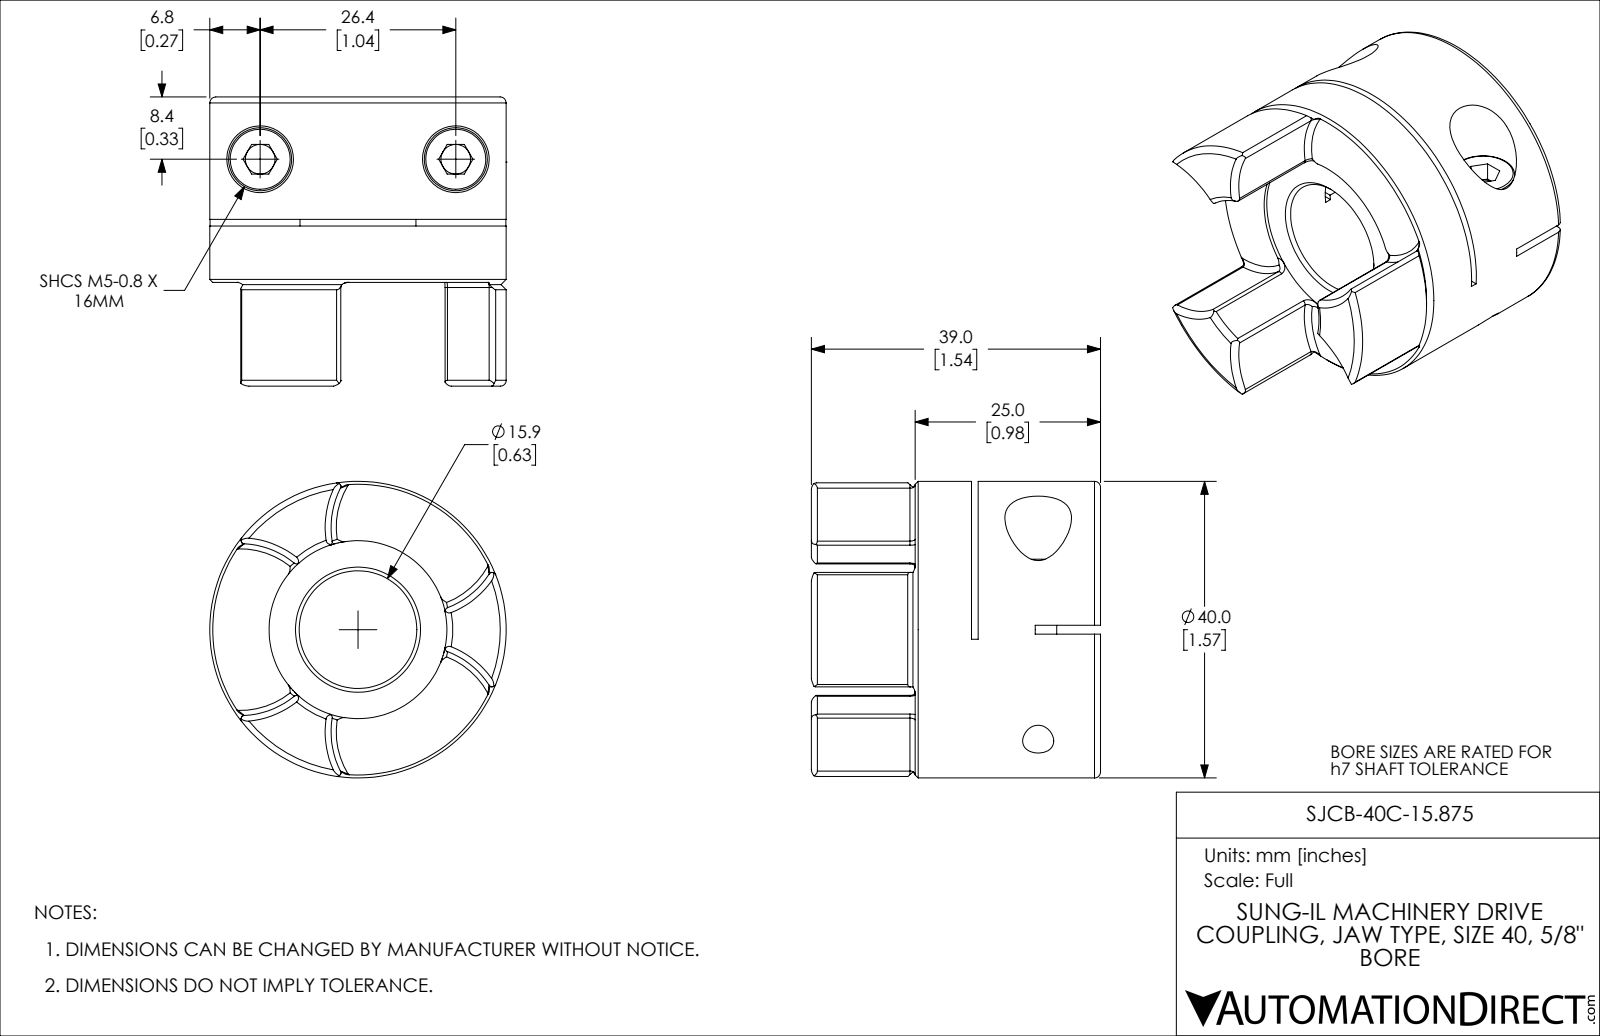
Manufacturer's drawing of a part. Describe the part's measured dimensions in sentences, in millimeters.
The part is named "SJCB-40C-15.875". Its 3-D file was written by "SolidWorks 2021 (CONFIG_CONTROL_DESIGN)". It is 3 solids with 184 faces: 50 planar, 68 cylindrical and 66 other. Overall it measures 40 by 40 by 39 millimeters. Its volume is 27 970 cubic millimeters and its surface area 11 590 square millimeters. Round holes: 2 of diameter 4, 2 of diameter 4.2, 2 of diameter 5.4, 2 of diameter 9, 1 of diameter 15.9, 1 of diameter 24. Round bosses or shafts: 2 of diameter 8.5, 2 of diameter 5, 1 of diameter 40. Partial cylindrical surfaces (rounded edges, fillets, slot ends): 12 of radius 0.5, 3 of radius 11.6, 1 of radius 40. The main face-to-face distances are 17.4, 0.9, 16.5, 7.6, 8.5, 25, 1.2, 0.5, 7.1, 8. The hole center spacings are 26.4.
